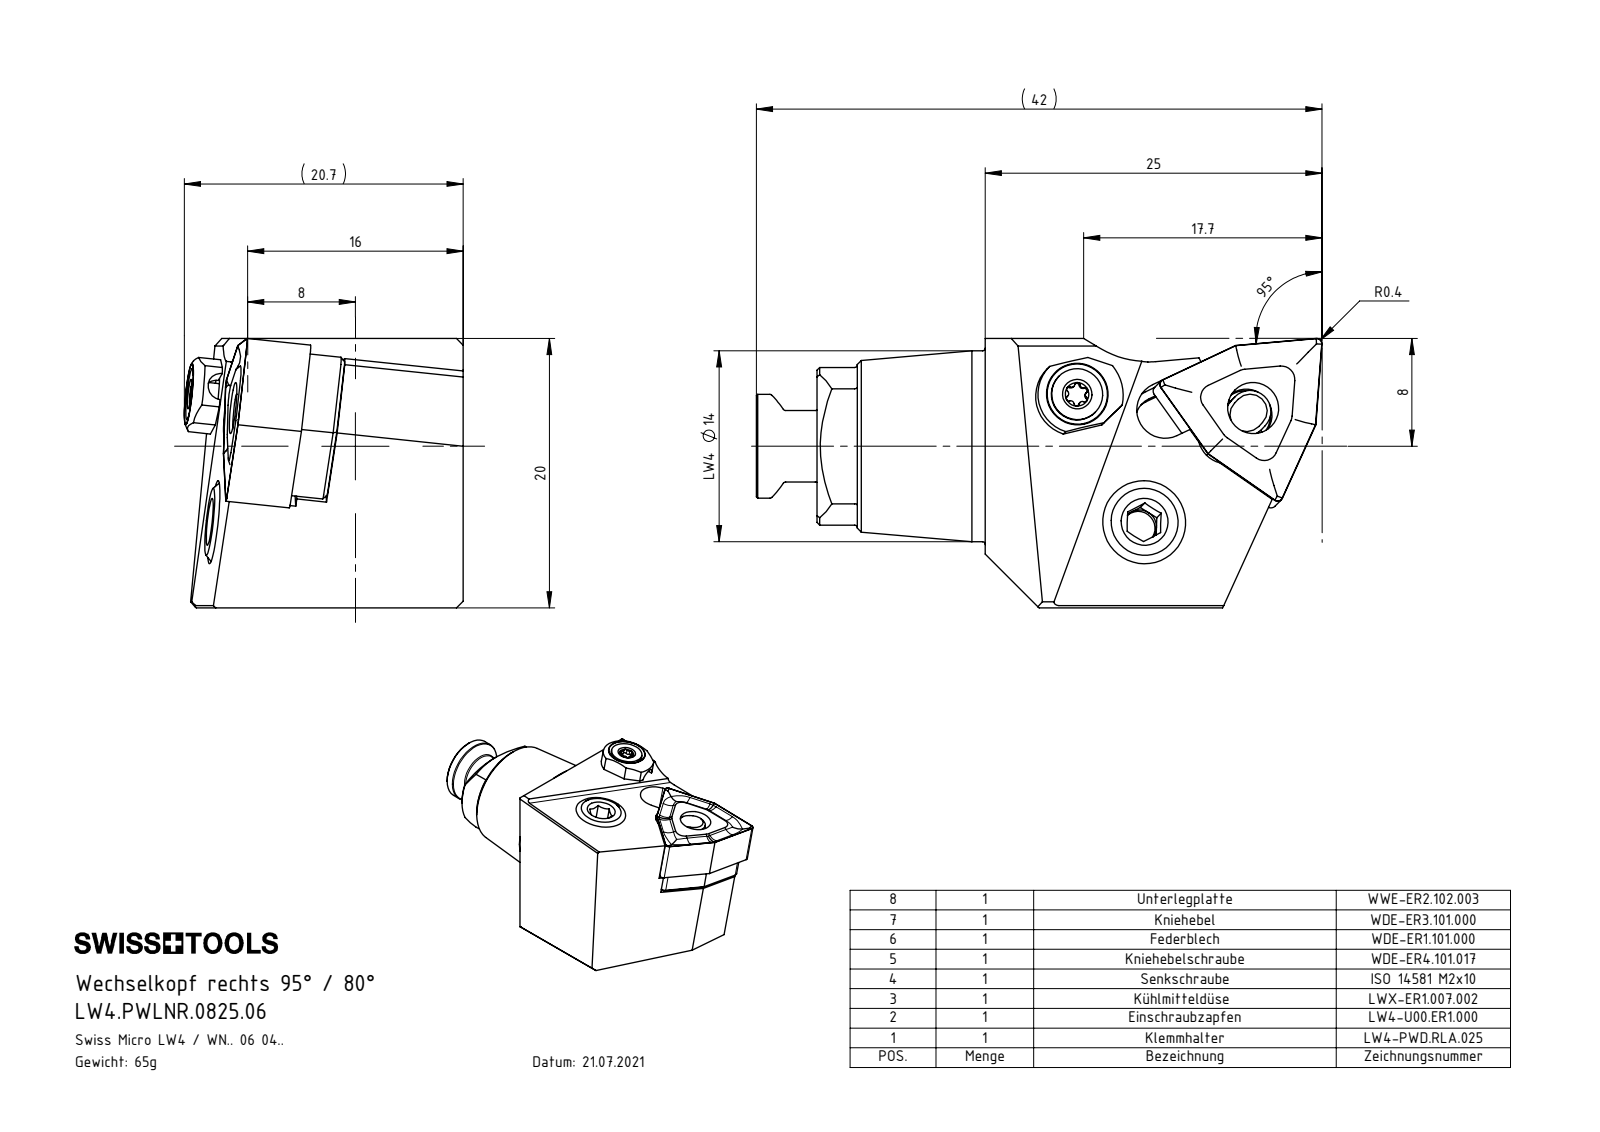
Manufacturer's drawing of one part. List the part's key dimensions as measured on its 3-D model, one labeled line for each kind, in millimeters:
Part name (STEP PRODUCT): WWD-ER3.001.000_A; WDE-ER1.101.000; LW4-PWD.RLA.025_B; LW4.PWLNR.0825.06 (+5 more)
STEP written by: SolidWorks 2022 (CONFIG_CONTROL_DESIGN)
Units: millimetres
Bodies: 8 solids, 401 faces (151 planar, 93 cylindrical, 157 other)
Overall size (bounding box): 42 × 20.7 × 20
Volume: 7 888 mm³ · Surface area: 5 282 mm²
Round holes (diameter × count): ⌀3 ×3, ⌀2.5 ×2, ⌀1.6 ×1, ⌀2 ×1, ⌀3.81 ×1, ⌀5 ×1, ⌀5.5 ×1, ⌀6.4 ×1
Round bosses / shafts (diameter × count): ⌀6 ×2, ⌀14.17 ×1, ⌀7.7 ×1, ⌀5.9 ×1, ⌀5.3 ×1, ⌀5 ×1, ⌀3.8 ×1, ⌀3.1 ×1
Partial cylindrical surfaces — rounded edges, fillets, slot ends (radius × count): R0.2 ×8, R0.24 ×6, R2.1 ×5, R0.4 ×3, R1 ×2, R0.5 ×1, R1.81 ×1, R2.2 ×1
Main face-to-face distances: 20, 4.2, 0.65, 7.19, 7.49, 7.5, 2, 1.86, 3, 4.7
Hole centre spacings: 10.64, 10.65, 11.81, 13.36
